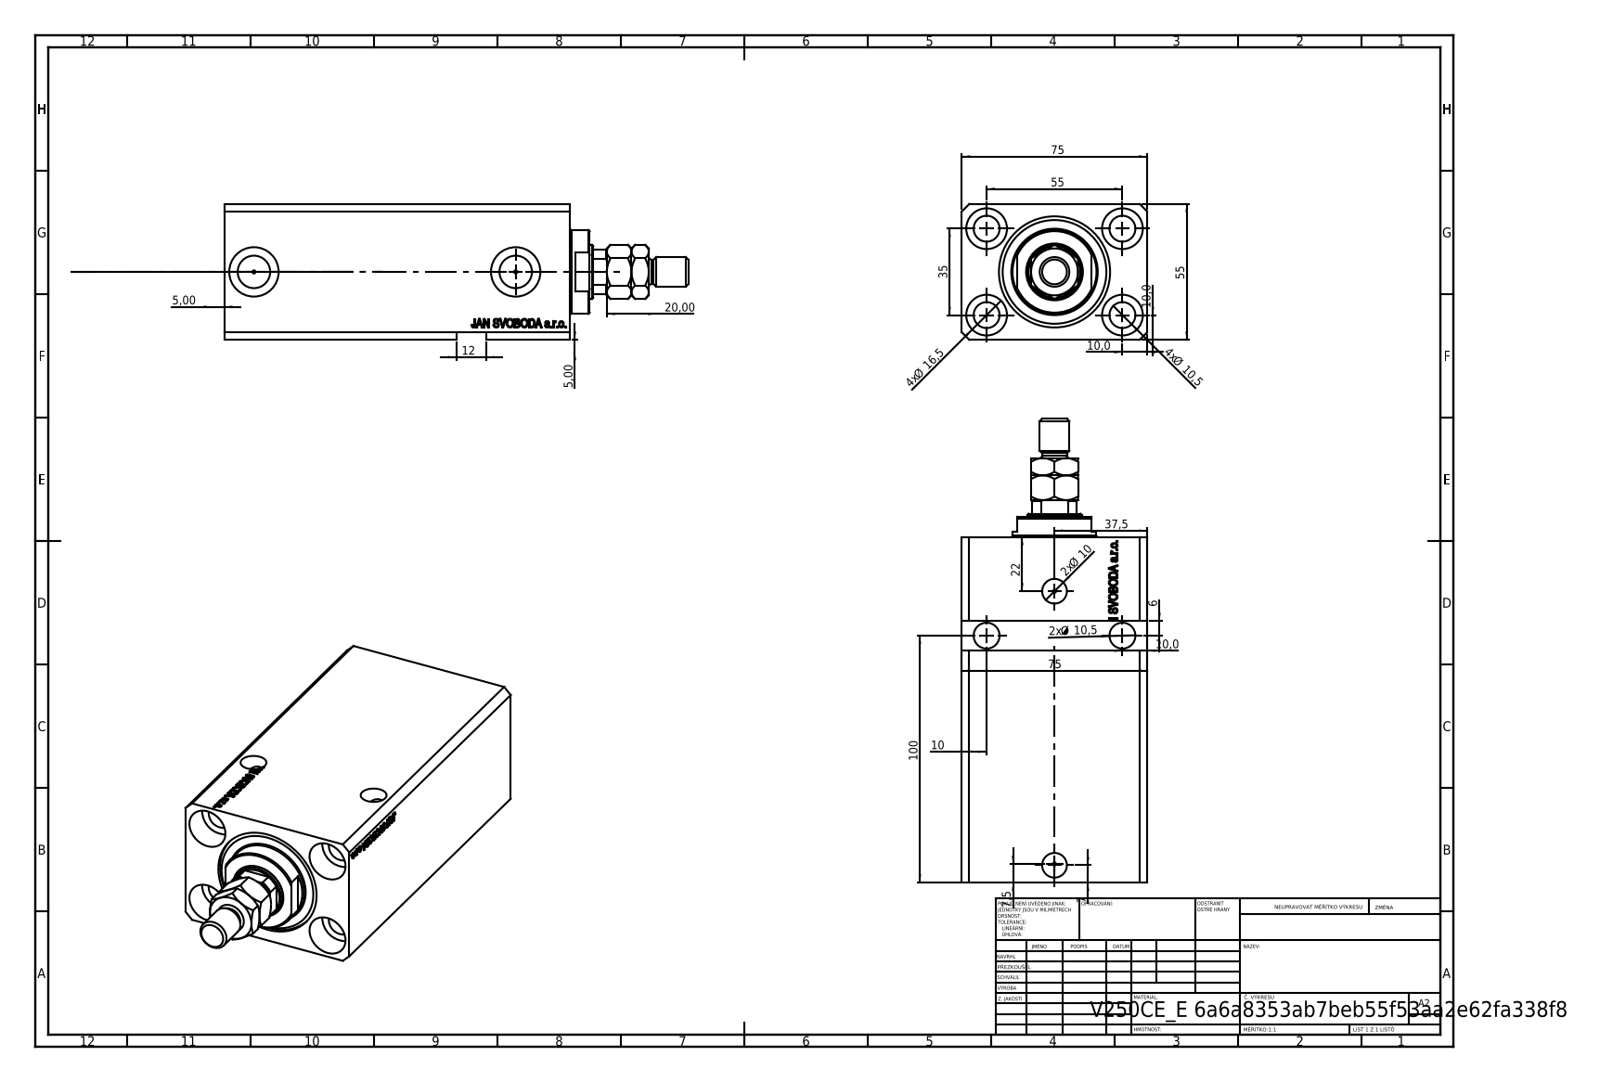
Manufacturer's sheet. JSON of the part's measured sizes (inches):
{"part_name": "V250CE_VC_E; MTA; V250CE_E_Body; V250CE_C_VCP", "step_written_by": "SolidWorks 2019 (CONFIG_CONTROL_DESIGN)", "units": "inches", "bodies": {"solids": 4, "faces": 943, "planar": 453, "cylindrical": 88, "other": 402}, "overall_size": [7.398, 2.953, 2.165], "volume_in3": 29.45, "surface_area_in2": 163.4, "round_holes": [[0.413, 7], [0.049, 4], [0.65, 4], [0.394, 2], [0.518, 2], [0.787, 2], [0.866, 1], [1.26, 1], [1.772, 1]], "round_bosses_or_shafts": [[1.339, 1], [0.472, 1], [0.394, 1]], "partial_cylinders_radius": [[0.413, 1]], "face_to_face_distances": [2.165, 2.953, 5.512, 4.445, 1.067, 0.39, 4.055, 5.122, 0.433, 5.079], "hole_center_spacings": [1.283, 2.165, 1.294, 1.378, 2.567, 3.798, 3.818, 0.021]}
